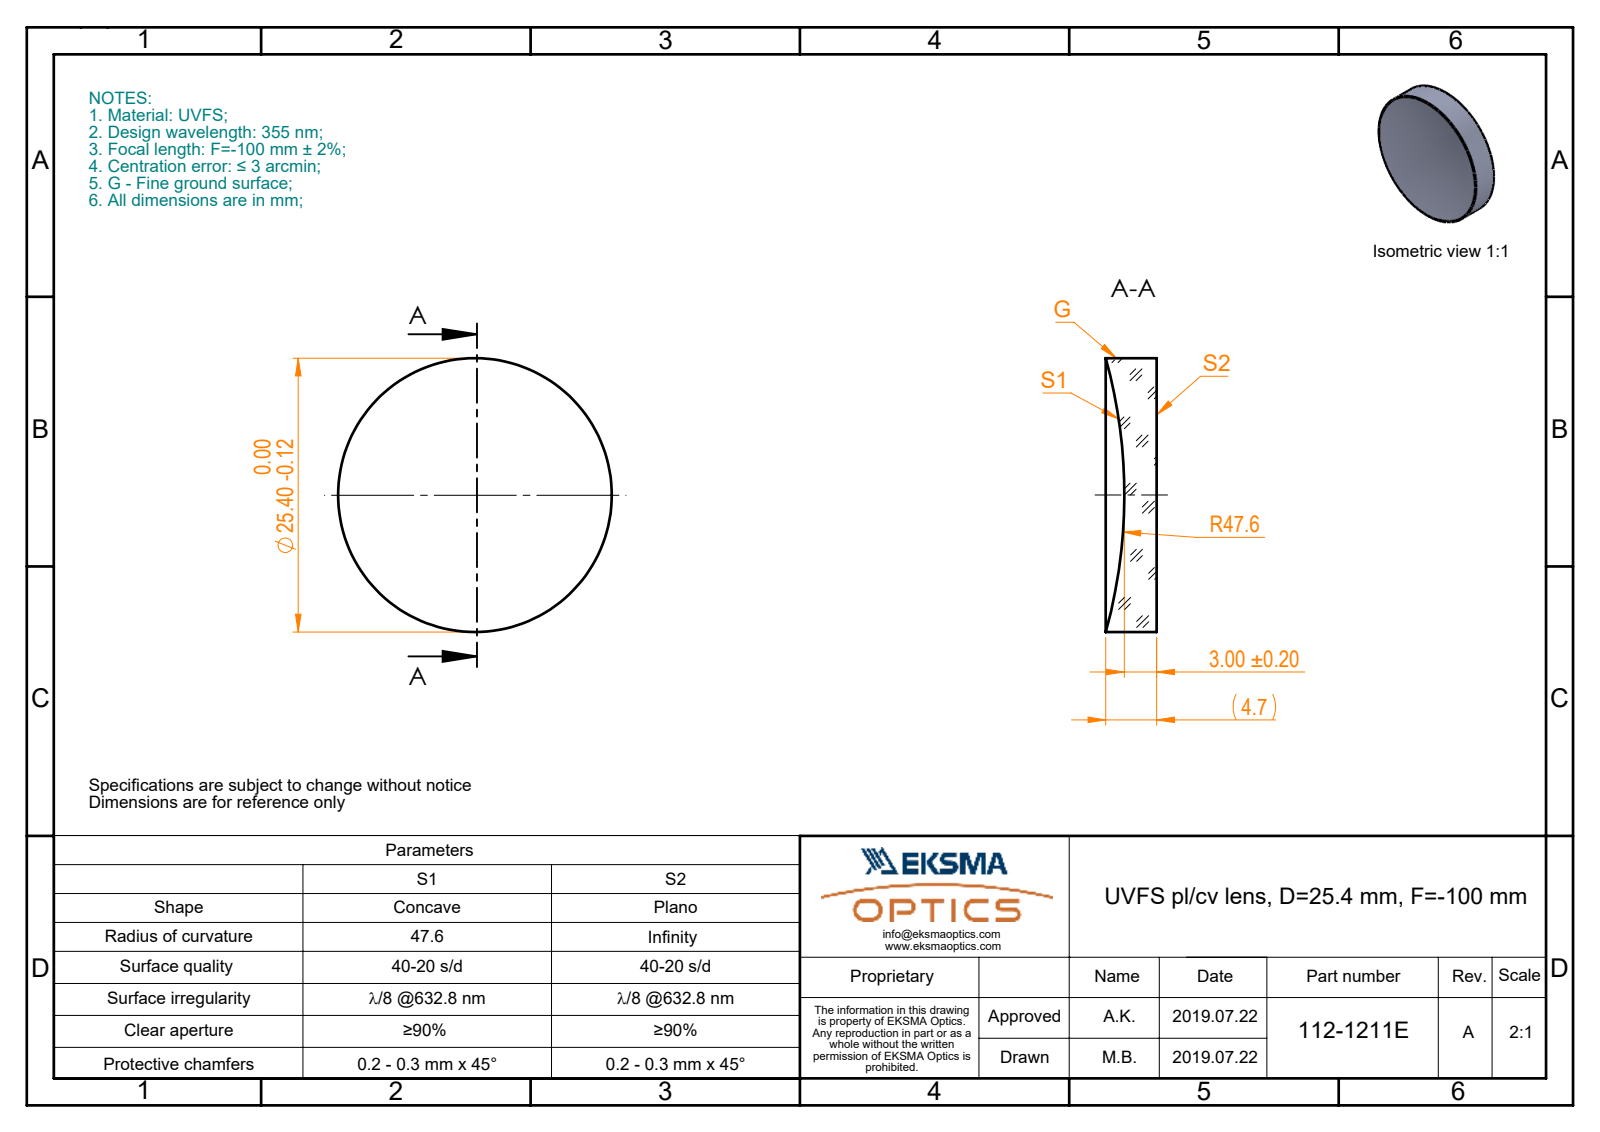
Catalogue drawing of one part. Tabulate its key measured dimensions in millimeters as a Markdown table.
| quantity | value |
| --- | --- |
| part name | 112-1211E UVFS pl-cv 25.4 F-100 |
| STEP written by | SolidWorks 2017 (CONFIG_CONTROL_DESIGN) |
| units | millimeters |
| bodies | 1 solid, 5 faces (1 planar, 2 cylindrical, 2 other) |
| overall size | 25.4 × 25.4 × 4.72 |
| volume | 1 954 mm³ |
| surface area | 1 400 mm² |
| round bosses / shafts (diameter × count) | 25.4 × 1 |
